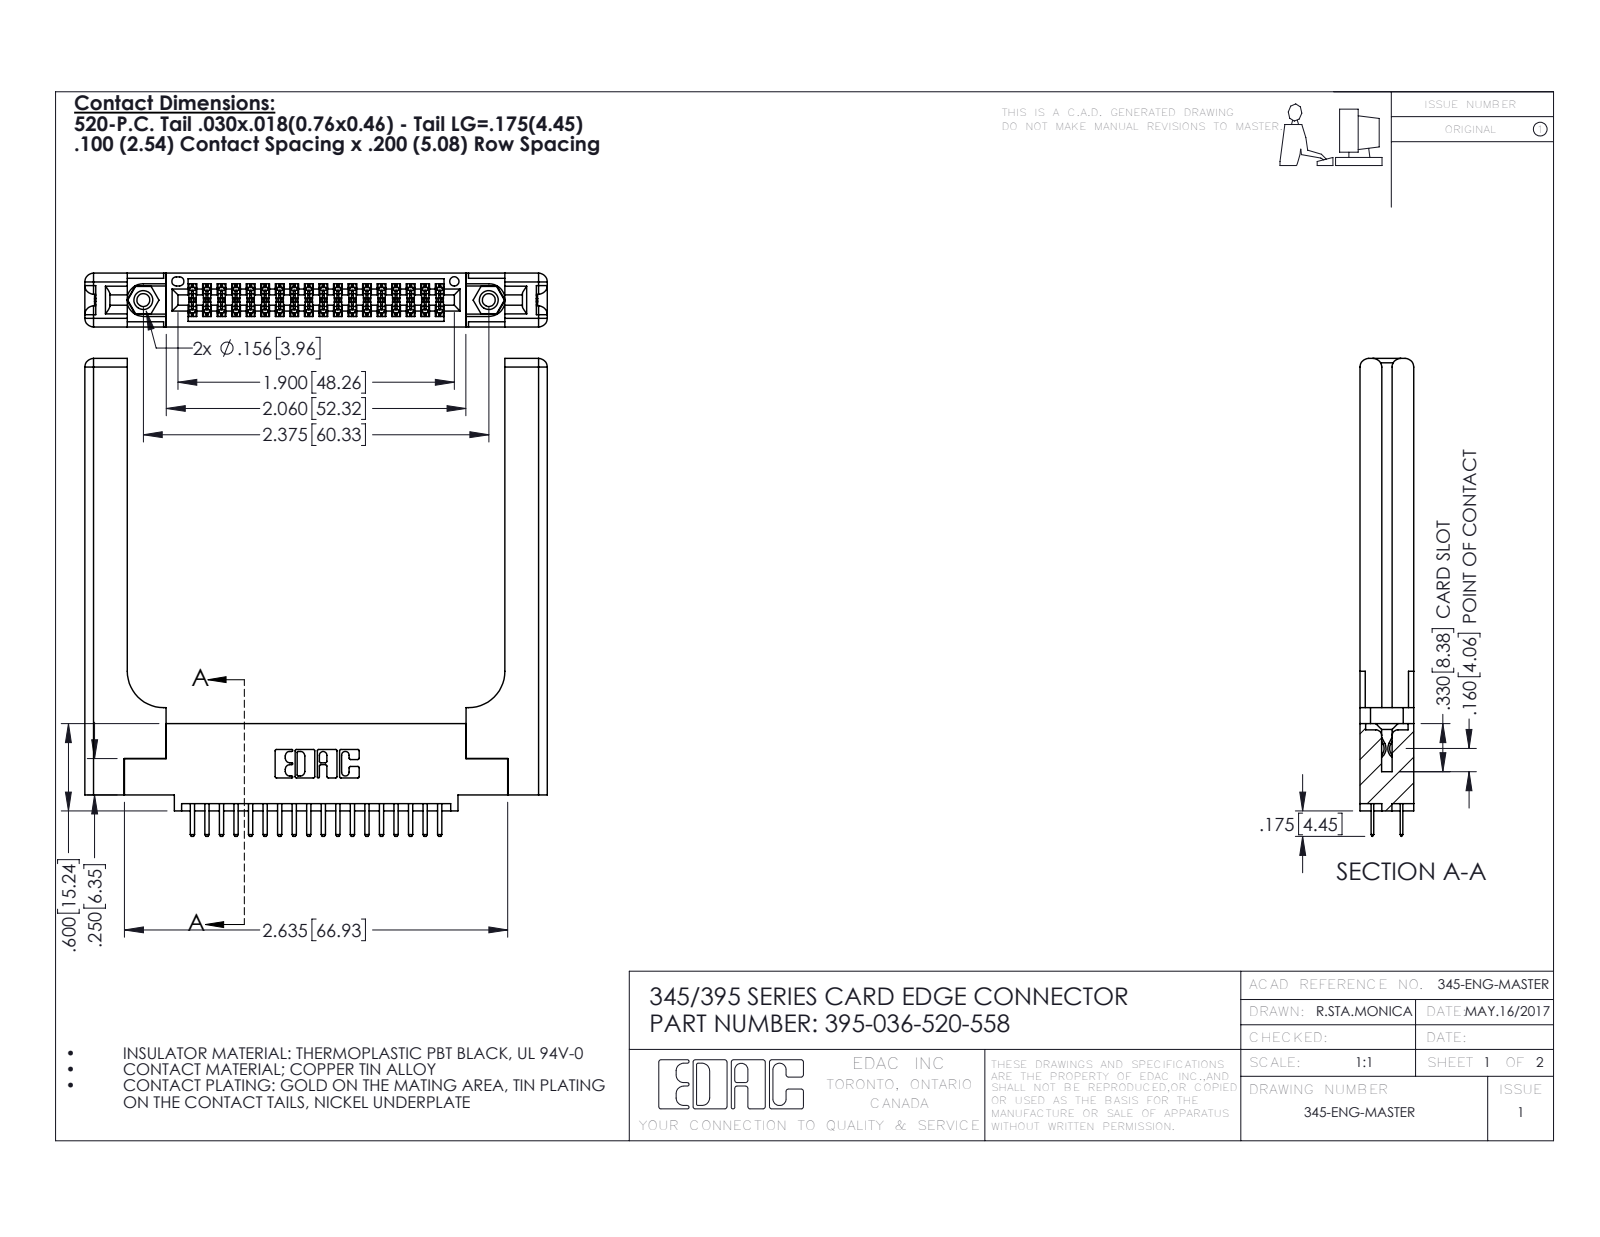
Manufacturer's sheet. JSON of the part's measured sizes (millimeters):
{"part_name": "345-250-001_345-250-001-102; 345-220-058_345-220-058; 345 Part_0.110 Offset - 0.156 Dia-TH; 345-292-001_345-293-120 (+1 more)", "step_written_by": "SolidWorks 2016 (CONFIG_CONTROL_DESIGN)", "units": "millimeters", "bodies": {"solids": 41, "faces": 2330, "planar": 1492, "cylindrical": 778, "other": 60}, "overall_size": [83.4, 80.7, 9.4], "volume_mm3": 16000, "surface_area_mm2": 15790, "round_holes": [[2.3, 2], [3.2, 2], [4, 2], [1.6, 1]], "round_bosses_or_shafts": [[3.9, 2]], "partial_cylinders_radius": [[0.2, 54], [0.3, 40], [0.3, 22], [1.5, 16], [0.2, 6], [0.8, 6], [0.7, 3], [0.4, 2]], "face_to_face_distances": [9.4, 1.8, 7.6, 3.8, 3.8, 5.1, 5.6, 2, 2.5, 6.9], "hole_center_spacings": [6.9, 54.4, 60.3]}
